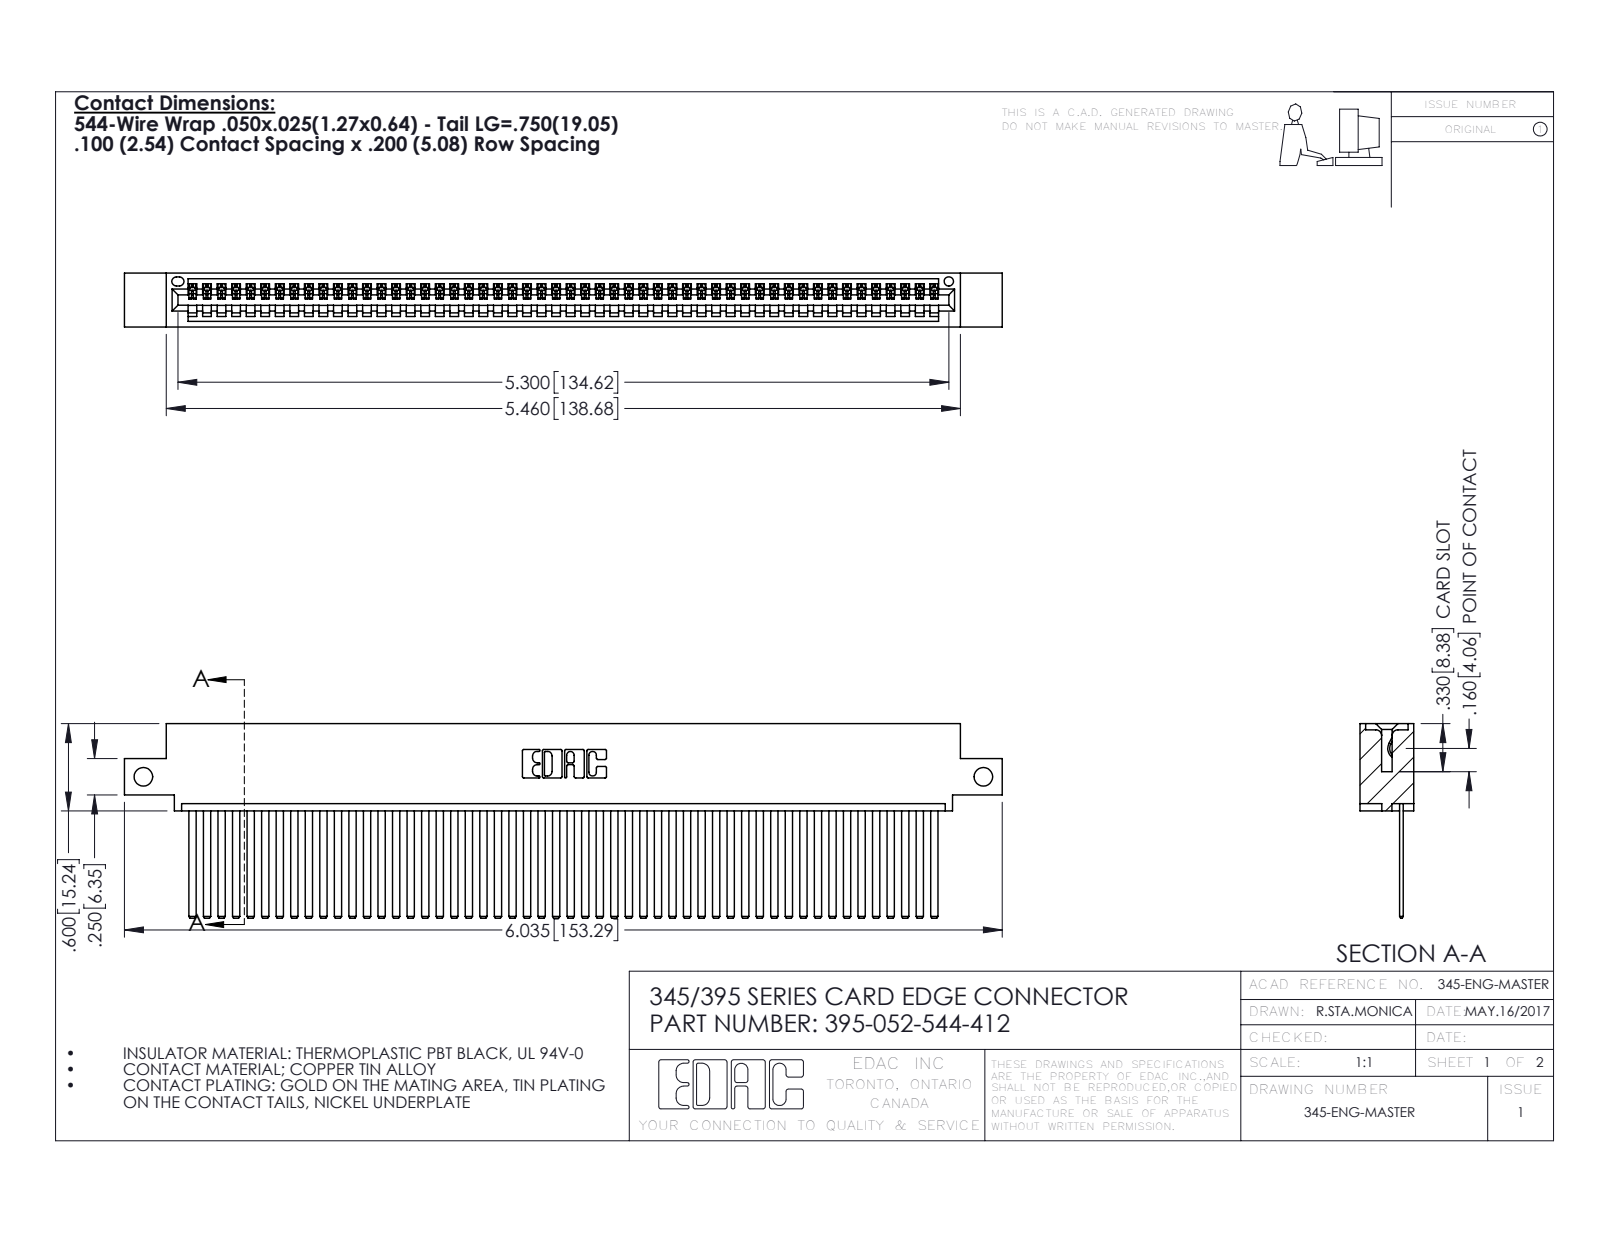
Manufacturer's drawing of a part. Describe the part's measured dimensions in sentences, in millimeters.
The part is named "345-292-001_345-293-144; 345 Part_0.110 Offset - Side Mount; 395-052-544-412". Its 3-D file was written by "SolidWorks 2016 (CONFIG_CONTROL_DESIGN)". It is 53 solids with 2834 faces: 1956 planar, 878 cylindrical and 0 other. Overall it measures 153.3 by 34 by 9.4 millimeters. Its volume is 15 100 cubic millimeters and its surface area 21 930 square millimeters. Round holes: 2 of diameter 3.3, 1 of diameter 1.6. Partial cylindrical surfaces (rounded edges, fillets, slot ends): 104 of radius 0.2, 22 of radius 0.3, 6 of radius 0.2, 6 of radius 0.8, 3 of radius 0.7, 2 of radius 0.8, 2 of radius 1, 1 of radius 0.4. The main face-to-face distances are 1.8, 7.6, 0.6, 2.5, 6.9, 9.4, 5.1, 5.7, 3.8, 1.8. The hole center spacings are 146.7.
